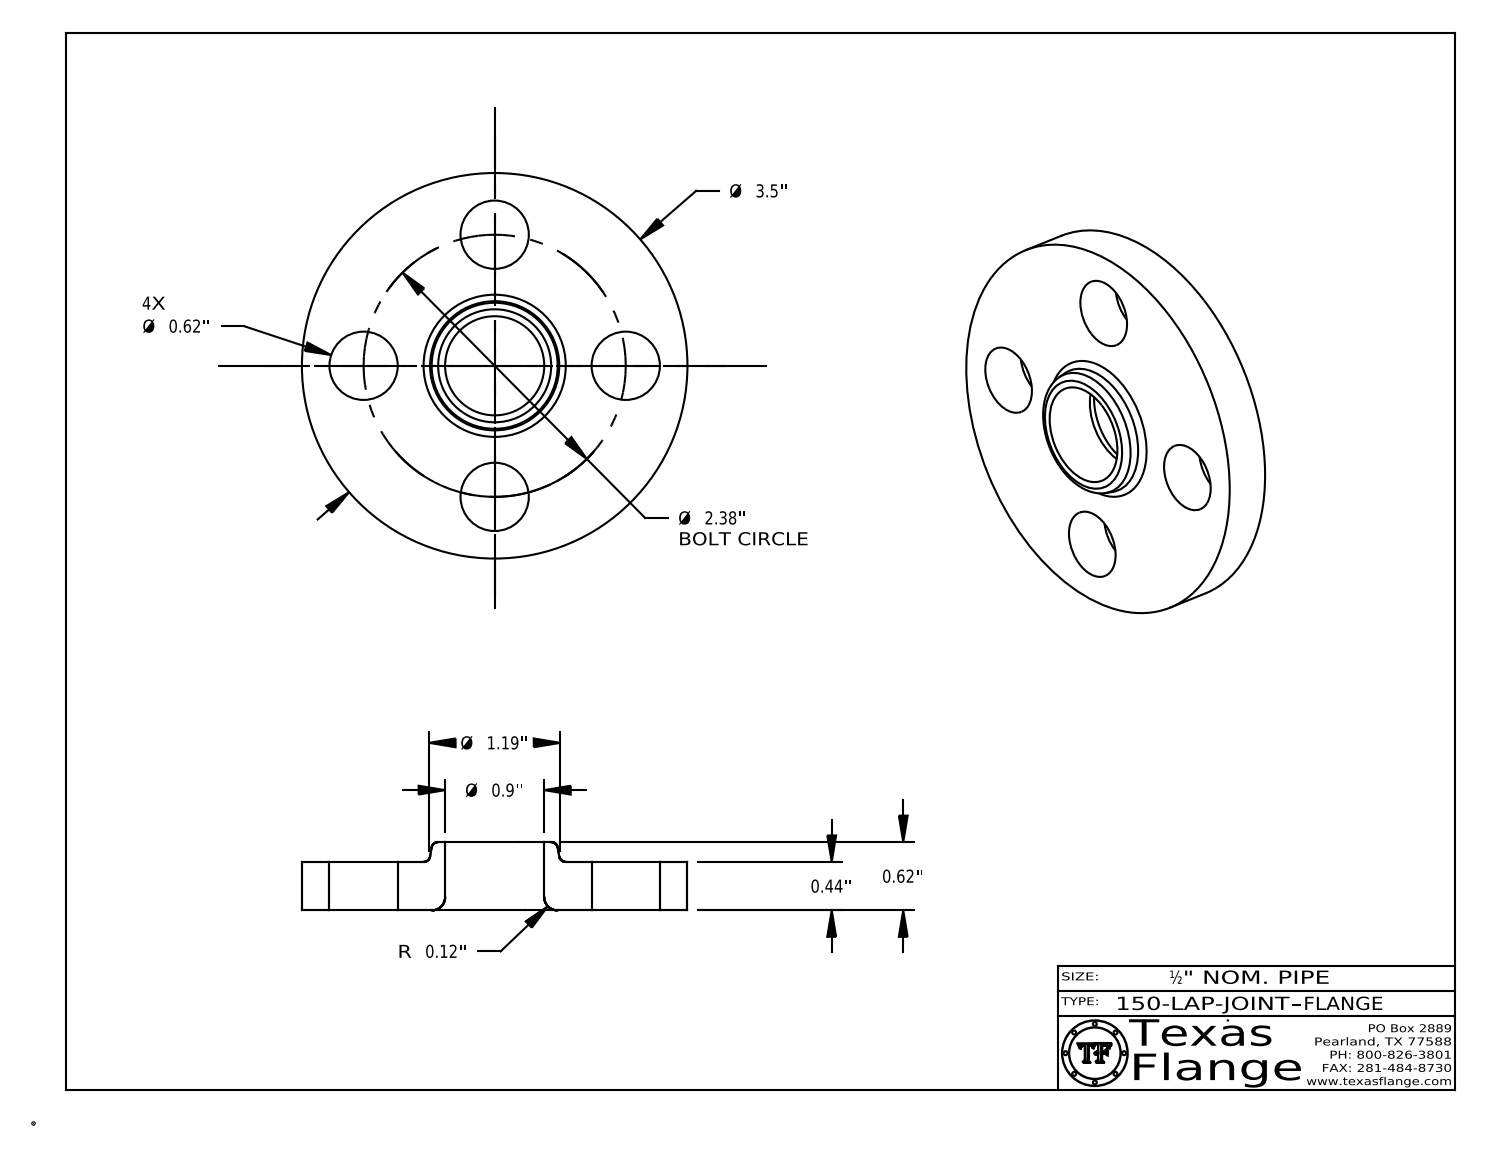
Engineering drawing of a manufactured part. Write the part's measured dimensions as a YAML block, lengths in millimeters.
part_name: "150-LAP-JOINT FLANGE"
step_written_by: "CATIA V5 STEP AP214 (AUTOMOTIVE_DESIGN)"
units: millimeters
bodies: {solids: 1, faces: 408, planar: 368, cylindrical: 32, other: 8}
overall_size: [88.9, 88.9, 15.7]
volume: 57140
surface_area: 16740
round_holes:
  - {diameter: 15.7, count: 4}
  - {diameter: 12.6, count: 1}
  - {diameter: 22.9, count: 1}
round_bosses_or_shafts:
  - {diameter: 0.8, count: 8}
  - {diameter: 88.9, count: 1}
  - {diameter: 9.9, count: 1}
face_to_face_distances: [11.2, 15.7, 4.6, 10.8, 0.4, 5, 3.8, 3.7, 0.7, 3.1]
hole_center_spacings: [30.2, 42.7, 23.1, 55.9, 60.5, 30.2]
